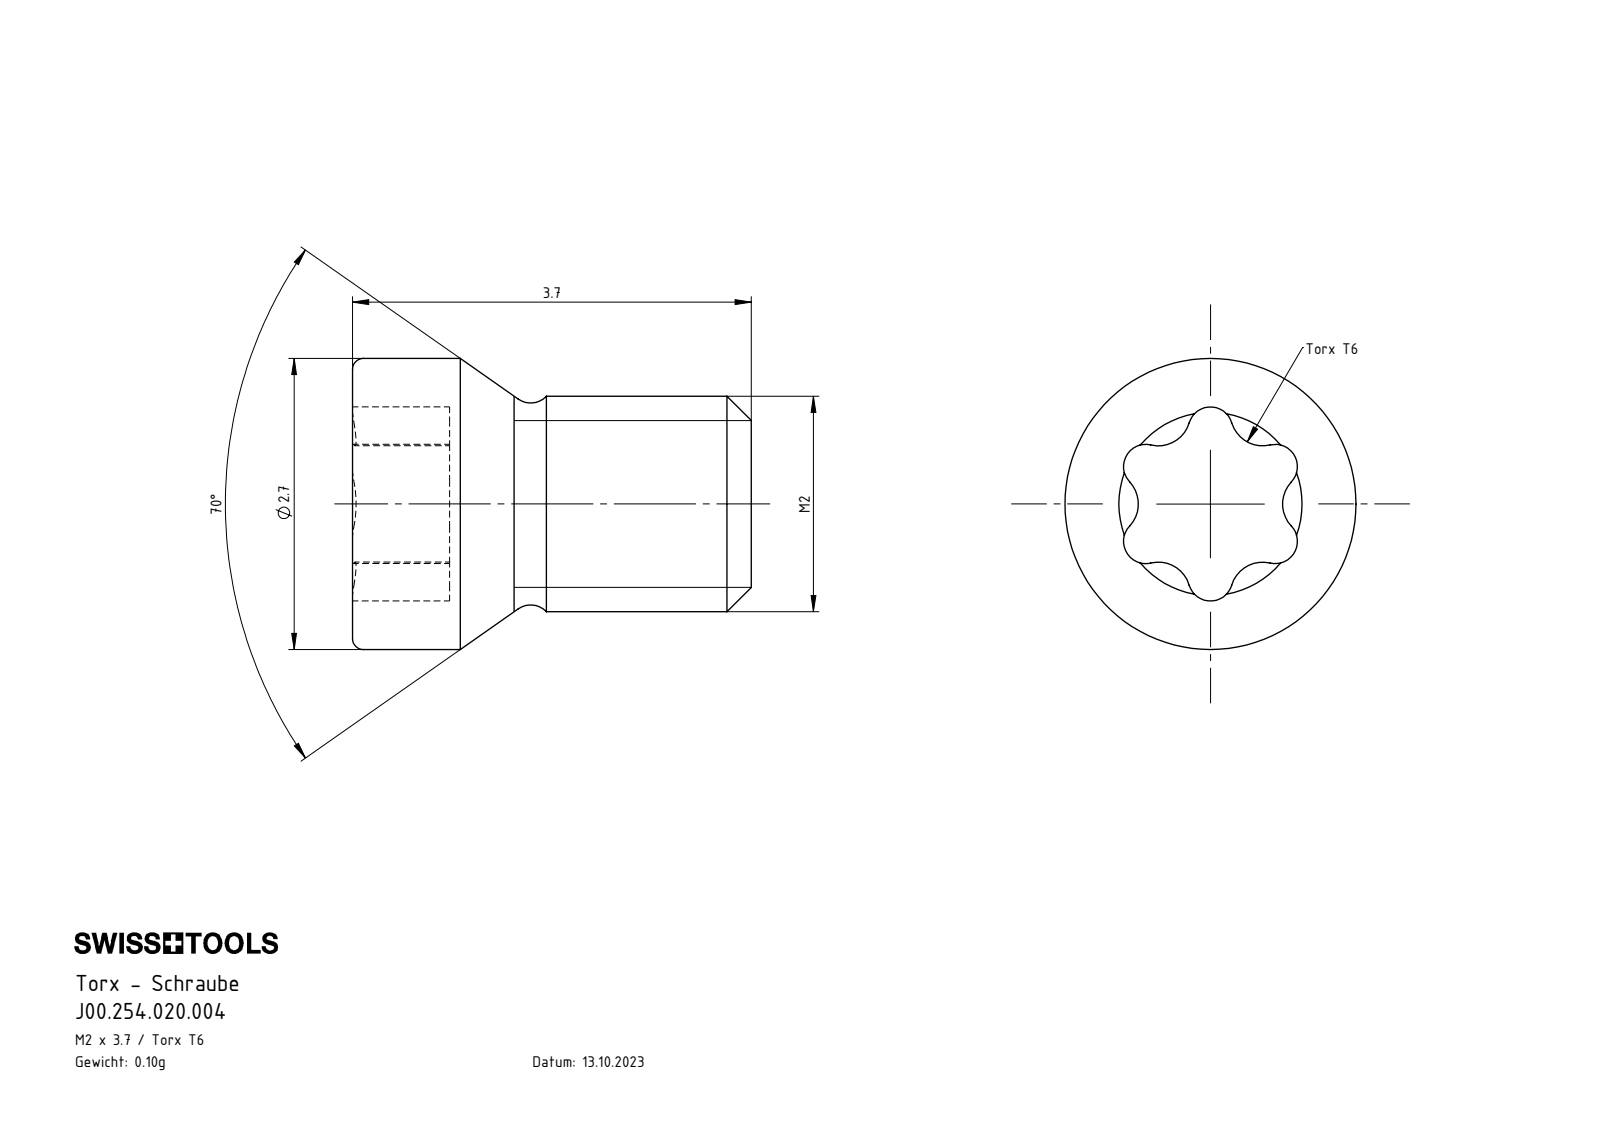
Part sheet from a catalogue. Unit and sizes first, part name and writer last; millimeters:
Units: millimetres
Overall size (bounding box): 3.7 × 2.7 × 2.7
Round bosses / shafts (diameter × count): ⌀2.7 ×1, ⌀2 ×1
Partial cylindrical surfaces — rounded edges, fillets, slot ends (radius × count): R0.21 ×6, R0.3 ×6
Main face-to-face distances: 0.9, 3.7, 2.8
Volume: 13 mm³ · Surface area: 40 mm²
Bodies: 1 solid, 41 faces (3 planar, 19 cylindrical, 19 other)
Part name (STEP PRODUCT): J00.254.020.004
STEP written by: SolidWorks 2022 (AUTOMOTIVE_DESIGN)
